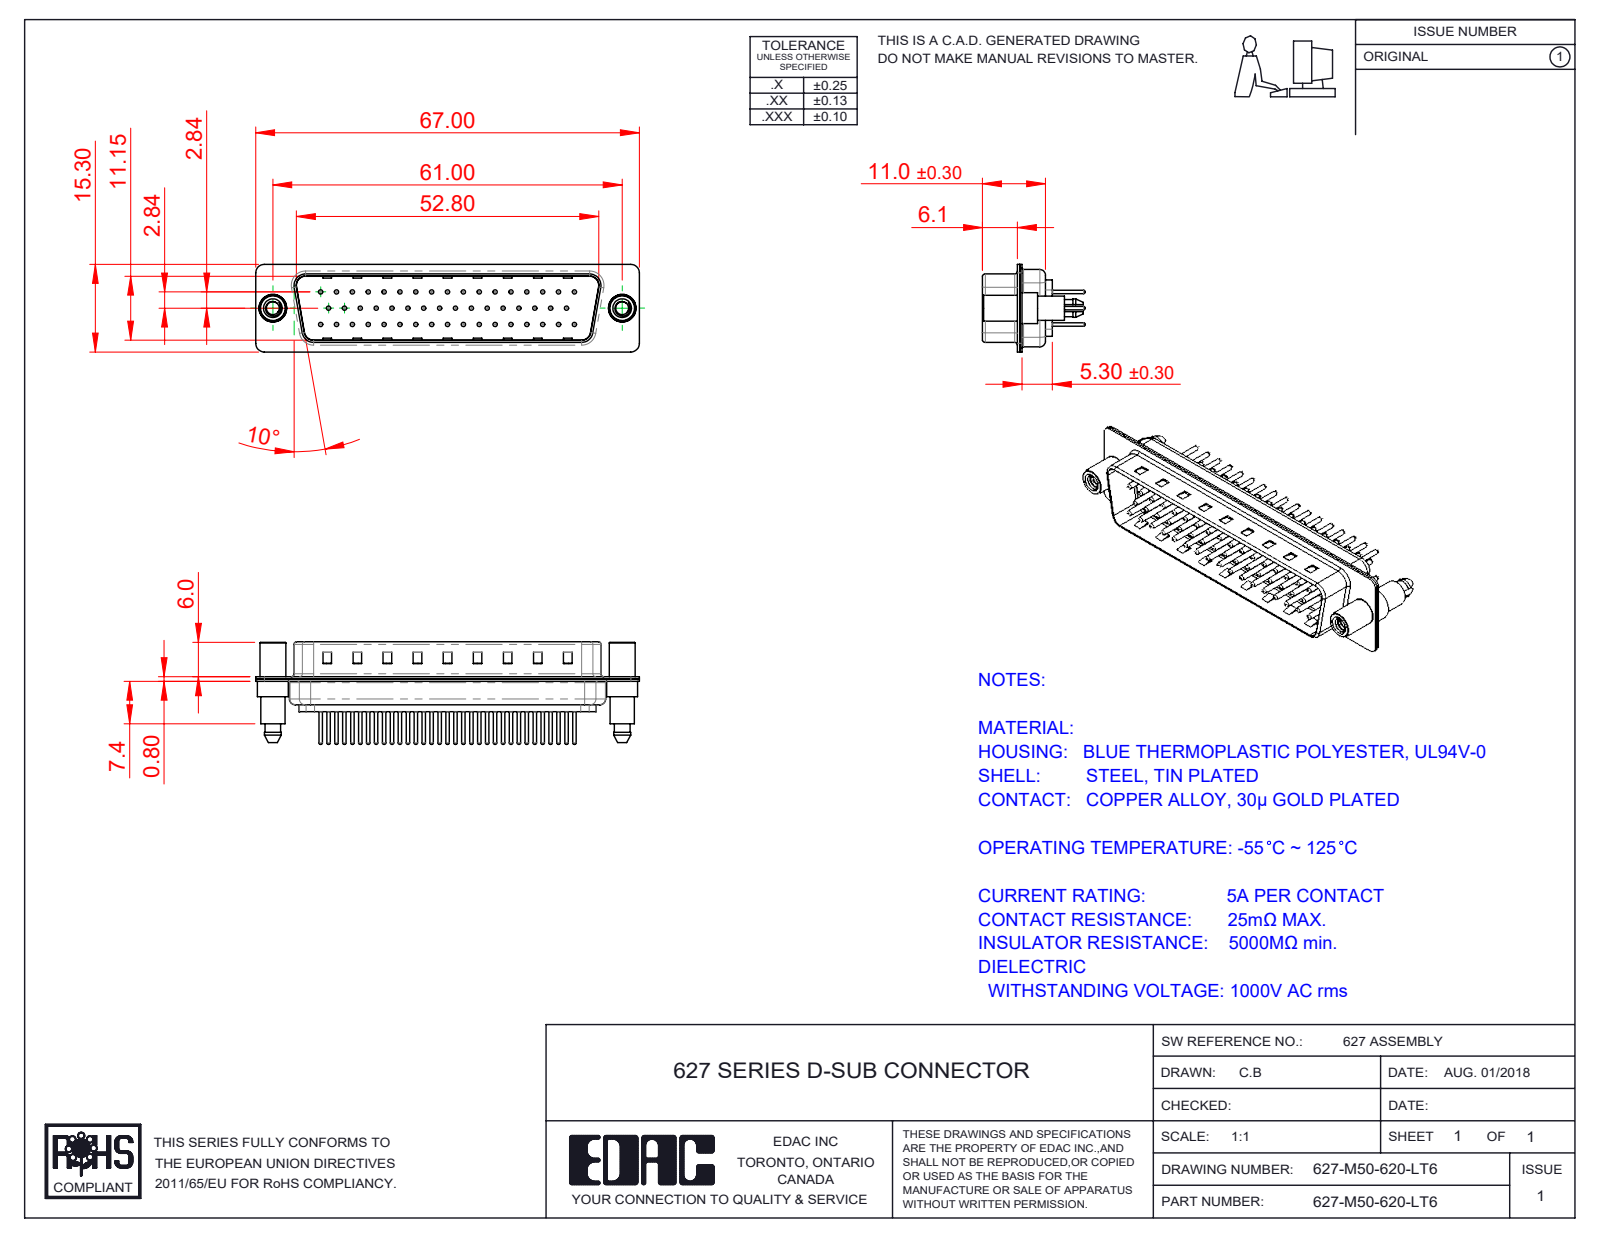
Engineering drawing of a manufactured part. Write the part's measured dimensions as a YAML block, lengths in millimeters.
part_name: "627M Contact Row 1_20; 627M Housing_50 Contacts; 627M Contact Row 3_20; 627M Shell Rear_50 Contacts (+4 more)"
step_written_by: "SolidWorks 2020 (CONFIG_CONTROL_DESIGN)"
units: millimeters
bodies: {solids: 55, faces: 2314, planar: 571, cylindrical: 869, other: 874}
overall_size: [67, 17.9, 15.3]
volume: 4863
surface_area: 11167
round_holes:
  - {diameter: 0.75, count: 50}
  - {diameter: 1.6, count: 50}
  - {diameter: 2, count: 50}
  - {diameter: 2.26, count: 2}
  - {diameter: 4, count: 2}
  - {diameter: 4.8, count: 2}
round_bosses_or_shafts:
  - {diameter: 1.5, count: 50}
  - {diameter: 0.6, count: 50}
  - {diameter: 5.4, count: 2}
  - {diameter: 4.9, count: 2}
  - {diameter: 4.5, count: 2}
  - {diameter: 4.25, count: 2}
partial_cylinders:
  - {radius: 1.5, count: 18}
  - {radius: 2, count: 12}
  - {radius: 1.6, count: 10}
  - {radius: 0.5, count: 8}
  - {radius: 0.25, count: 4}
  - {radius: 0.6, count: 4}
  - {radius: 0.65, count: 4}
  - {radius: 0.9, count: 4}
face_to_face_distances: [0.4, 11.55, 5.7, 6.1, 0.78, 0.77, 12.33, 5.3, 12.32, 13.1]
hole_center_spacings: [3.16, 2.77, 5.54, 8.31, 11.08, 13.85, 16.62, 5.03]
